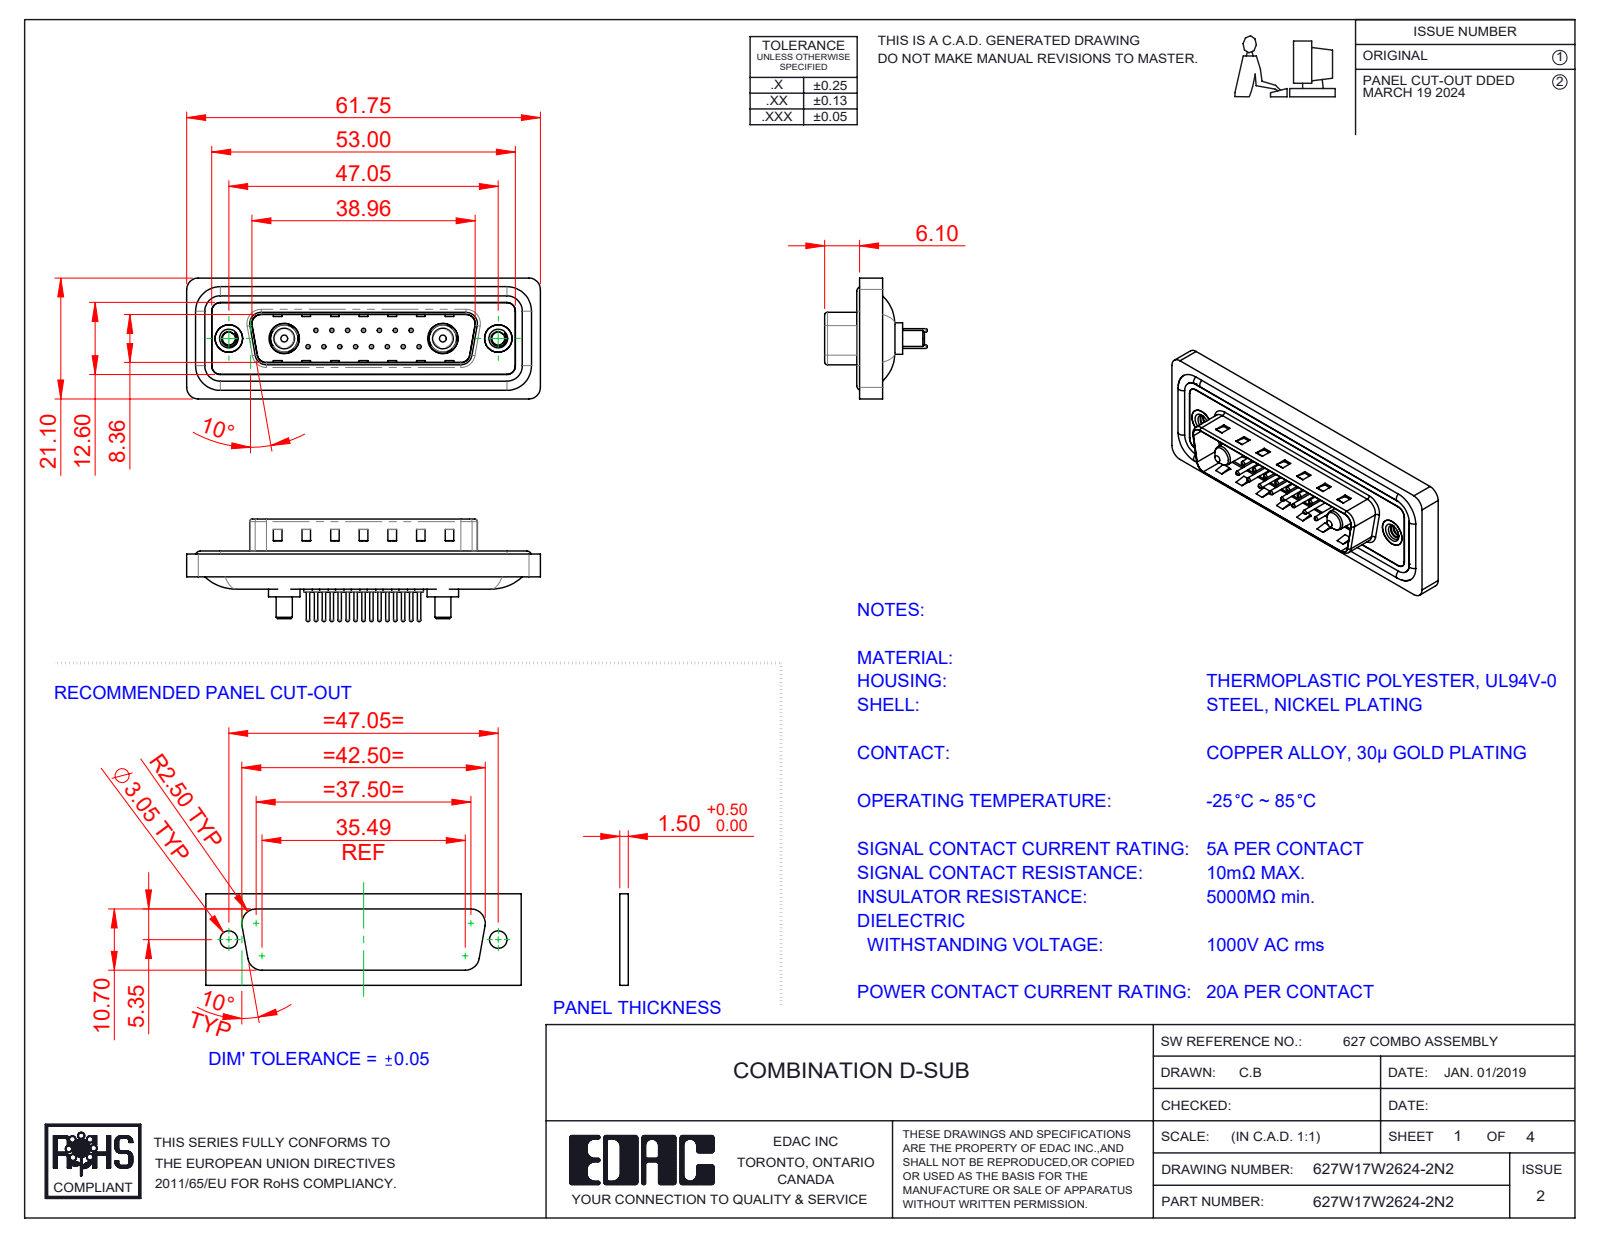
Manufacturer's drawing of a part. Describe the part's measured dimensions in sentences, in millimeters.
The part is named "627Combo Shell Rear_25 Contacts; 627Combo Housing_17W2; 627Combo Contact Row 1_24; 627Combo Shell Front_25 Contacts (+5 more)". Its 3-D file was written by "SolidWorks 2023 (CONFIG_CONTROL_DESIGN)". It is 26 solids with 1116 faces: 334 planar, 436 cylindrical and 346 other. Overall it measures 61.75 by 21.1 by 17.9 millimeters. Its volume is 7 266 cubic millimeters and its surface area 11 914 square millimeters. Round holes: 15 of diameter 0.75, 15 of diameter 1.6, 15 of diameter 2, 2 of diameter 2.26, 2 of diameter 4, 2 of diameter 4.8, 2 of diameter 4.85, 2 of diameter 5, 2 of diameter 5.3. Round bosses or shafts: 15 of diameter 1.5, 15 of diameter 0.6, 4 of diameter 1.6, 2 of diameter 5.5, 2 of diameter 5.2, 2 of diameter 4.9, 2 of diameter 4.75, 2 of diameter 3.75. Partial cylindrical surfaces (rounded edges, fillets, slot ends): 22 of radius 1.5, 18 of radius 2, 8 of radius 0.5, 8 of radius 1.6, 4 of radius 0.25, 4 of radius 0.6, 4 of radius 0.65, 4 of radius 0.9. The main face-to-face distances are 0.4, 1.5, 1.1, 1.6, 0.5, 3.1, 2.9, 0.82, 9.58, 4.1. The hole center spacings are 3.16, 2.77, 5.54, 8.31, 5.04, 7.49, 11.08, 5.03.
